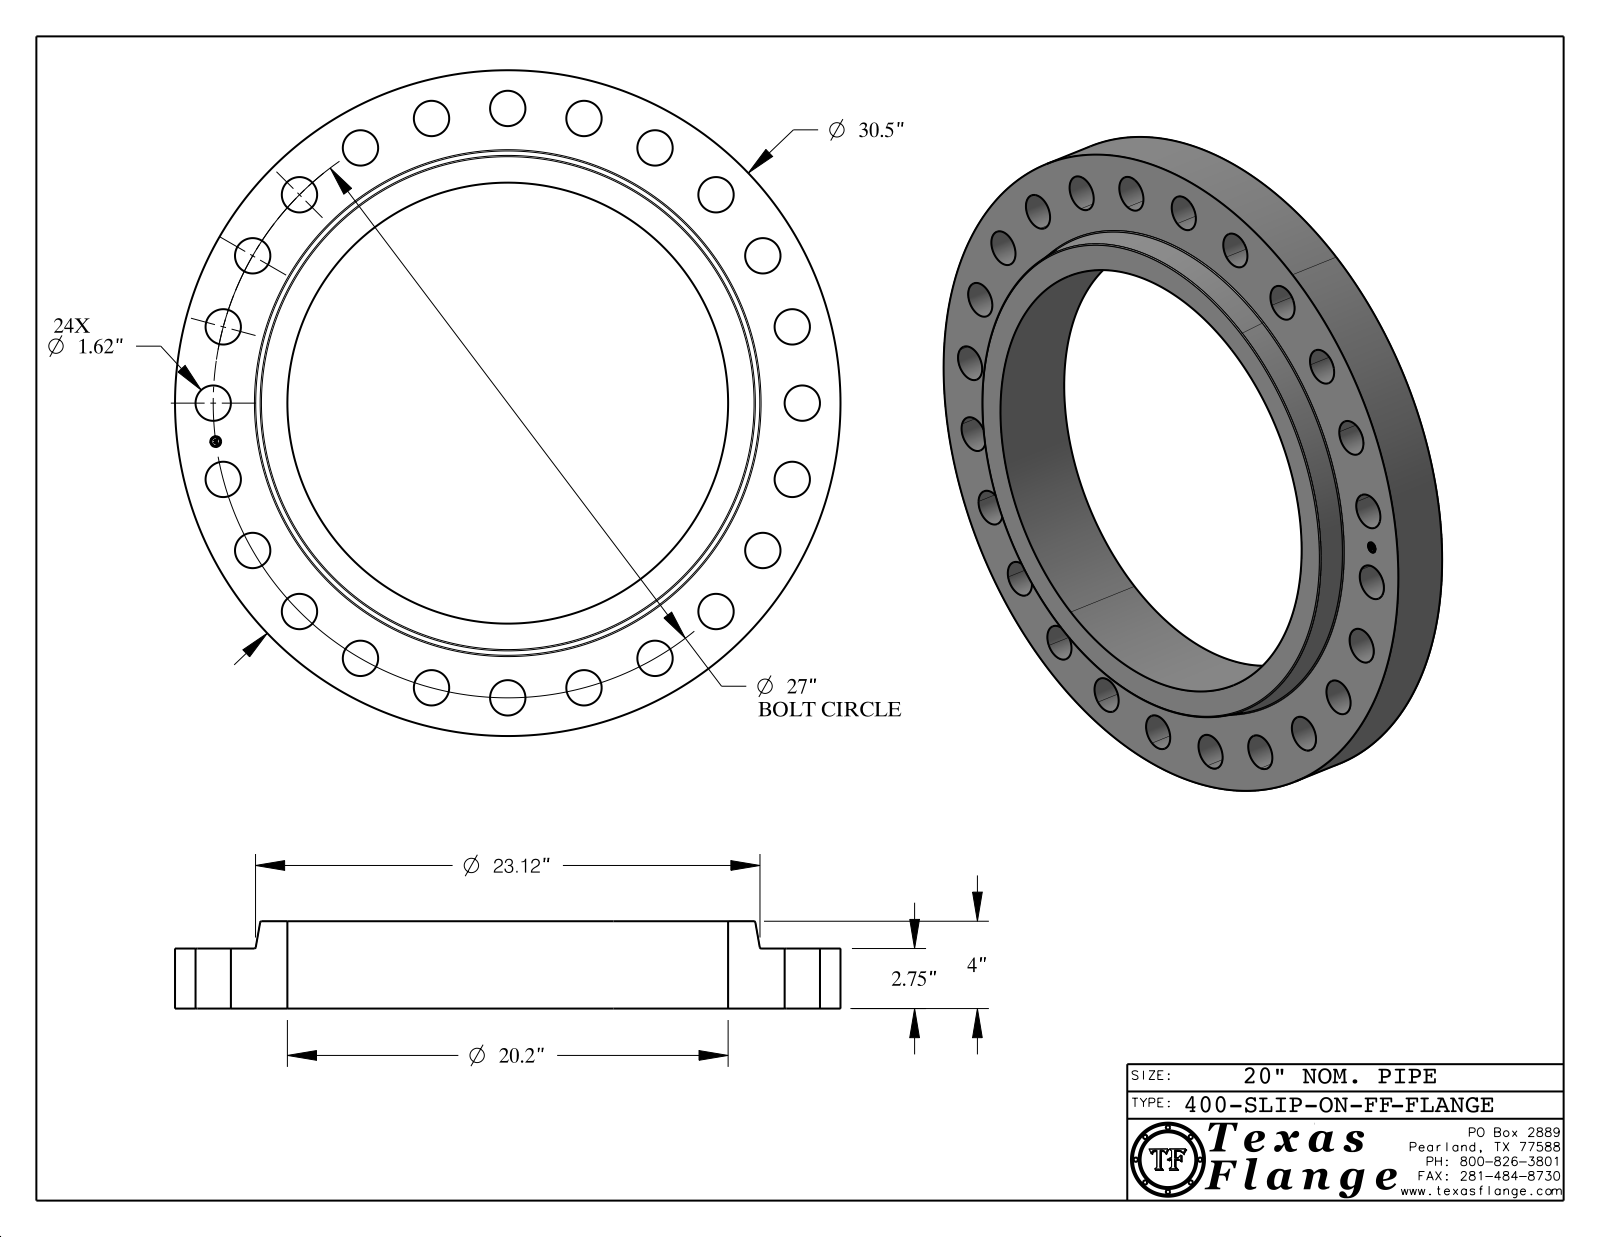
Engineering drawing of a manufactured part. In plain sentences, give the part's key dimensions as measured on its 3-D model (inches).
The part is named "400-SLIP-ON-FF". Its 3-D file was written by "CATIA V5 STEP AP214 (AUTOMOTIVE_DESIGN)". It is 1 solid with 446 faces: 368 planar, 72 cylindrical and 6 other. Overall it measures 30.5 by 30.5 by 4 inches. Its volume is 1 106 cubic inches and its surface area 1 648 square inches. Round holes: 24 of diameter 1.62, 1 of diameter 0.495, 1 of diameter 20.2. Round bosses or shafts: 8 of diameter 0.03, 1 of diameter 30.5, 1 of diameter 0.39. The main face-to-face distances are 2.75, 4, 1.25, 2.735, 0.015, 1.265, 0.148, 0.144, 0.027, 0.096. The hole center spacings are 13.5, 3.524, 6.988, 10.333, 16.437, 24.945, 26.769, 21.421.
